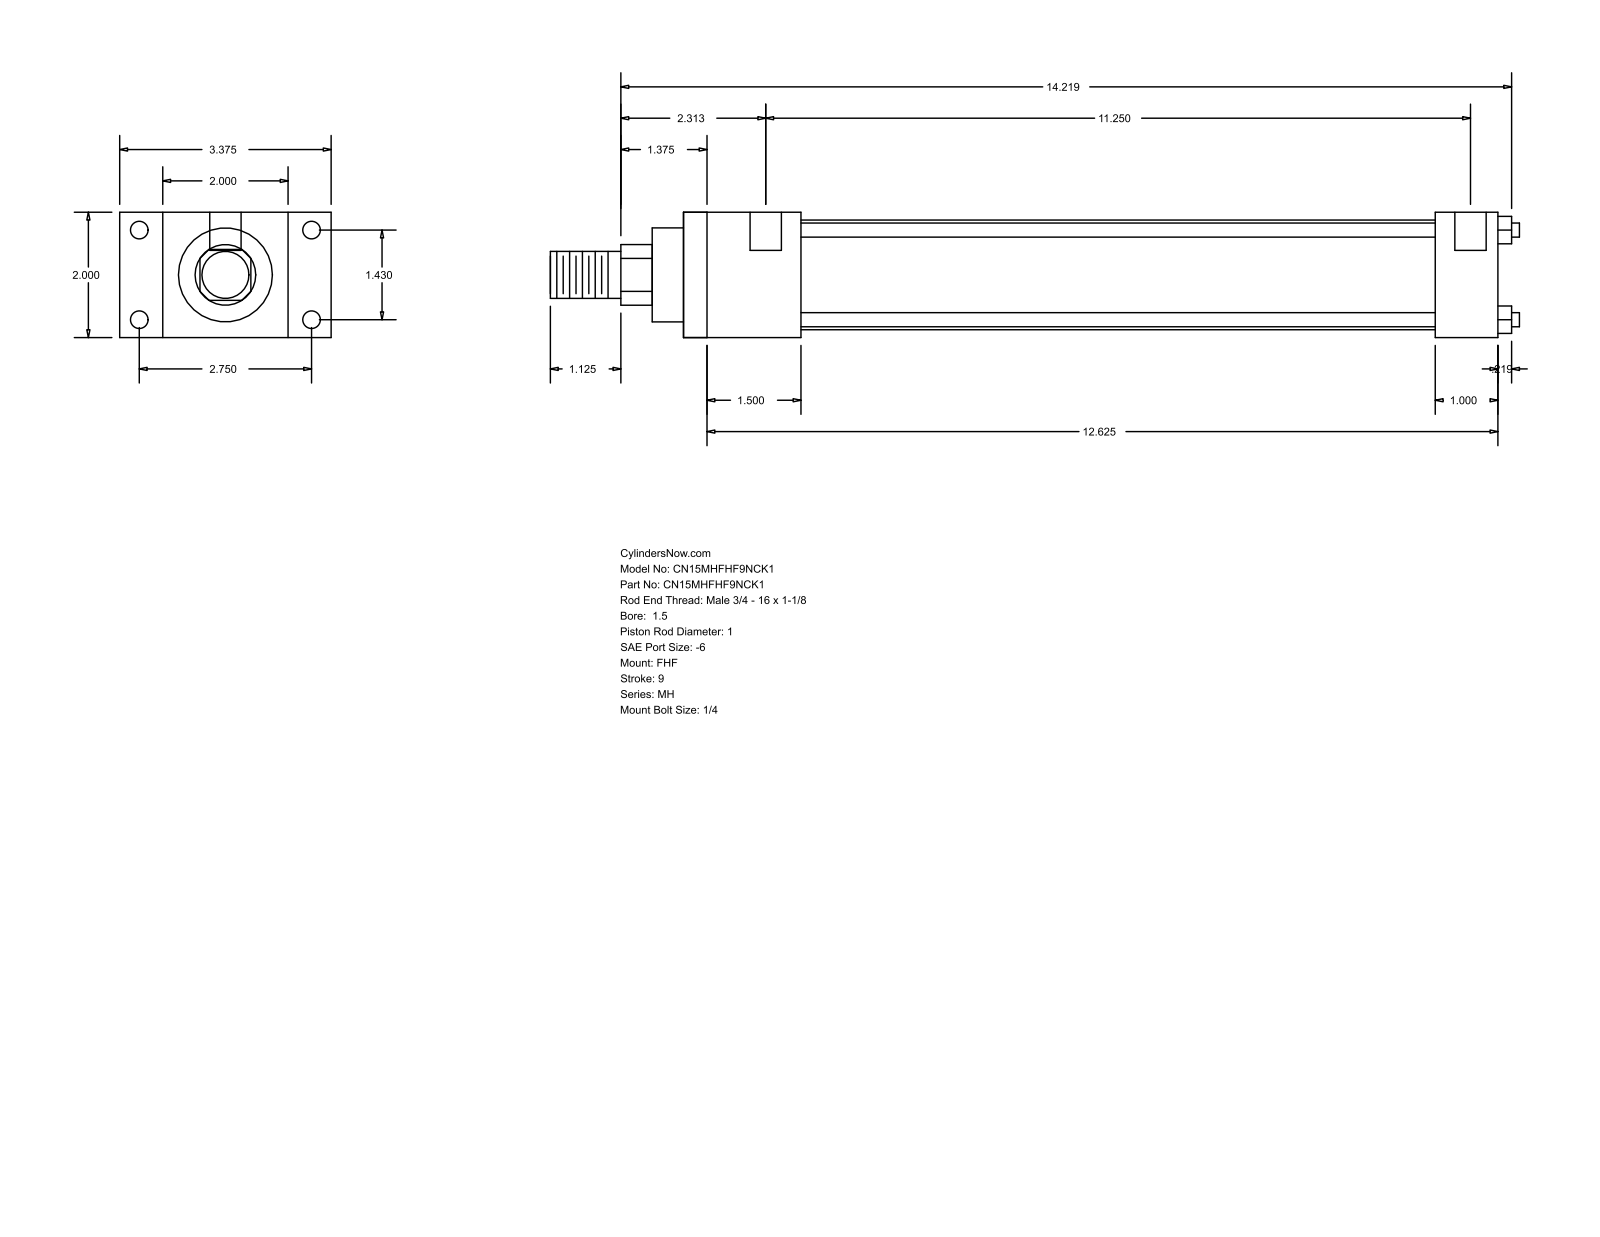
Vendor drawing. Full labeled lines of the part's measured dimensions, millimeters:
Part name (STEP PRODUCT): MH_FHF__0150_1
STEP written by: GSSL Pune (CONFIG_CONTROL_DESIGN)
Units: millimetres
Bodies: 0 solids, 88 faces (60 planar, 28 cylindrical, 0 other)
Overall size (bounding box): 392.91 × 85.72 × 50.8
Round holes (diameter × count): ⌀5.56 ×4, ⌀7.14 ×4, ⌀12.7 ×2
Round bosses / shafts (diameter × count): ⌀5.71 ×4, ⌀44.45 ×1, ⌀38.1 ×1, ⌀25.4 ×1, ⌀19.05 ×1
Partial cylindrical surfaces — rounded edges, fillets, slot ends (radius × count): R12.29 ×1
Main face-to-face distances: 50.8, 17.46, 68.26, 47.63, 85.72, 330.2, 282.57, 25.4, 304.8, 257.17
Hole centre spacings: 36.32, 69.84, 78.72, 288.93, 3.18, 285.75
